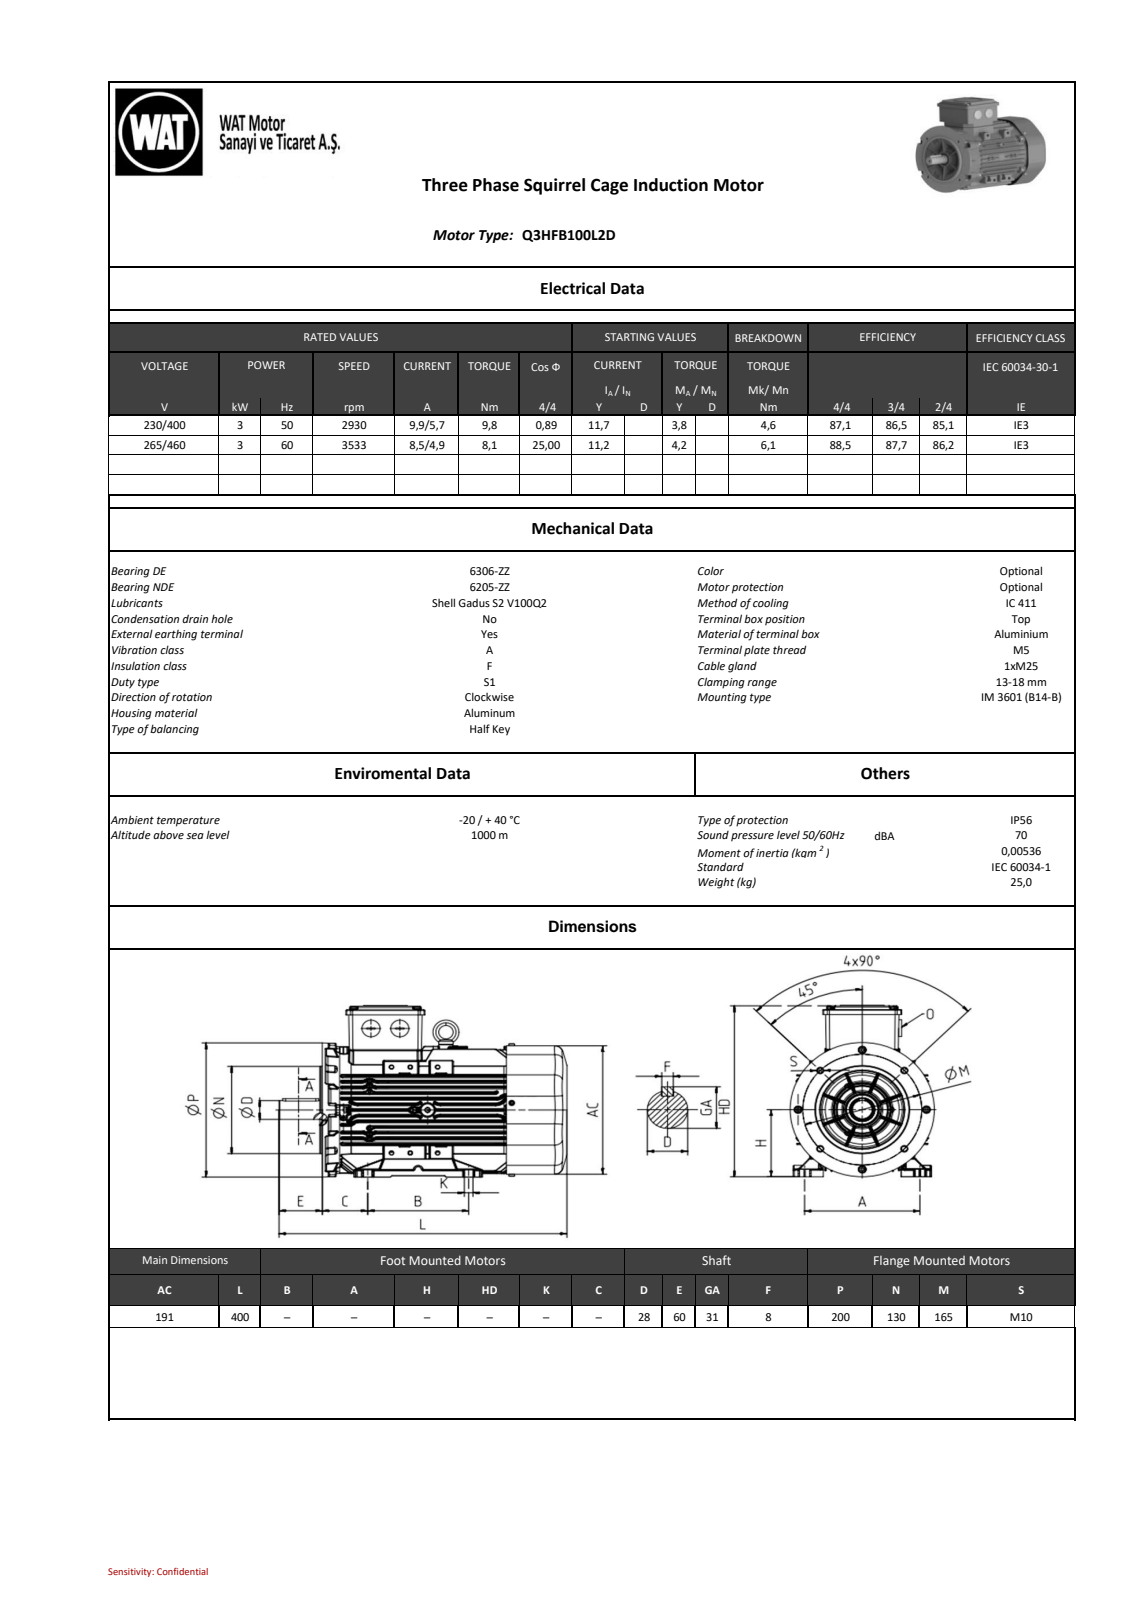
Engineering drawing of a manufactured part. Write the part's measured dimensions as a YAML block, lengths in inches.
part_name: "QH series_ 100_B14b_stp_objects"
step_written_by: "SIEMENS PLM Software NX2206.8101 (AUTOMOTIVE_DESIGN)"
units: inches
bodies: {solids: 0, faces: 5610, planar: 1204, cylindrical: 2205, other: 2201}
overall_size: [15.721, 10.068, 7.874]
round_holes:
  - {diameter: 0.335, count: 4}
  - {diameter: 0.394, count: 1}
  - {diameter: 1.749, count: 1}
  - {diameter: 2.26, count: 1}
  - {diameter: 3.504, count: 1}
  - {diameter: 4.291, count: 1}
  - {diameter: 5.079, count: 1}
  - {diameter: 5.236, count: 1}
round_bosses_or_shafts:
  - {diameter: 0.315, count: 8}
  - {diameter: 0.197, count: 4}
  - {diameter: 0.984, count: 3}
  - {diameter: 5.118, count: 1}
  - {diameter: 4.469, count: 1}
  - {diameter: 3.681, count: 1}
  - {diameter: 2.391, count: 1}
  - {diameter: 1.181, count: 1}
partial_cylinders:
  - {radius: 0.031, count: 633}
  - {radius: 0.039, count: 578}
  - {radius: 0.02, count: 81}
  - {radius: 0.079, count: 77}
  - {radius: 0.032, count: 52}
  - {radius: 0.197, count: 40}
  - {radius: 0.591, count: 26}
  - {radius: 0.118, count: 16}
face_to_face_distances: [0.336, 0.333, 0.333, 3.002, 0.666, 3.679, 1.007, 0.671, 3.019, 2.348]
hole_center_spacings: [3.248, 4.594, 6.496]
